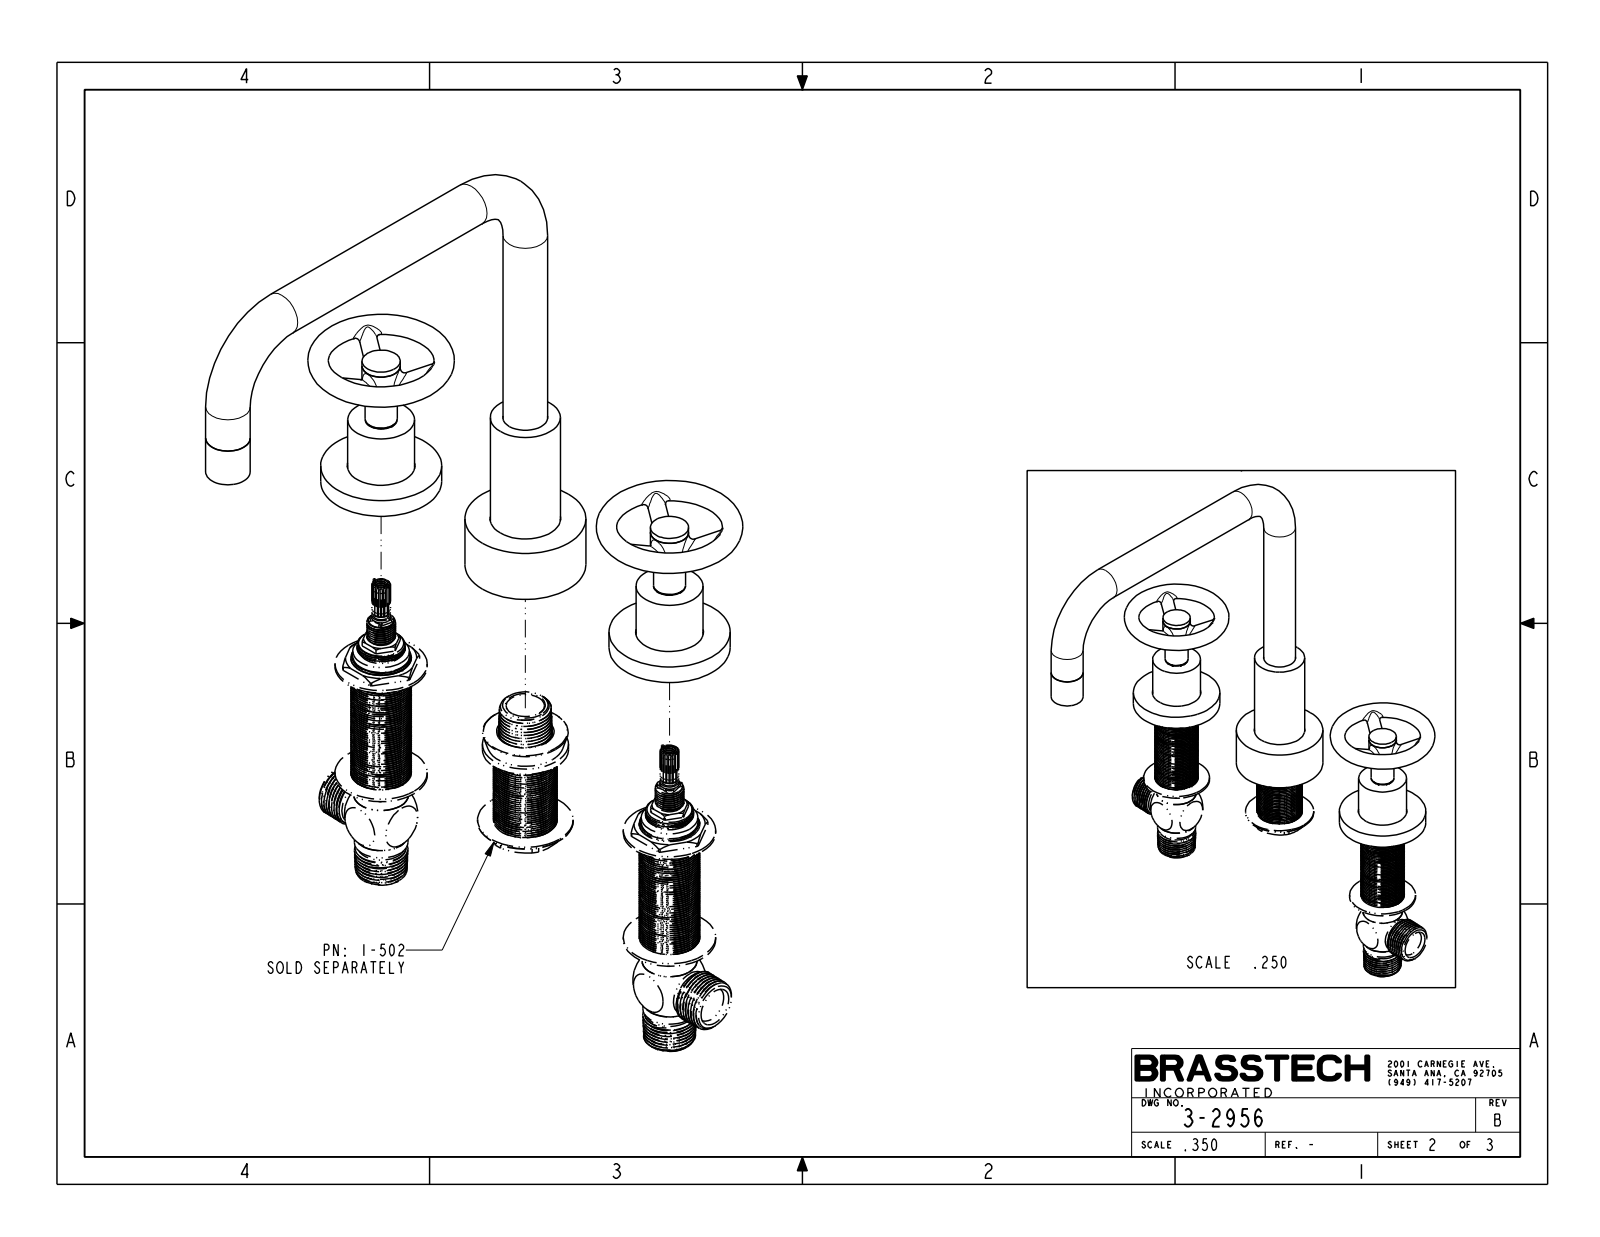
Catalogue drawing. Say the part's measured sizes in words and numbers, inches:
The part is named "3-2956". Its 3-D file was written by "CREO PARAMETRIC BY PTC INC, 2018400 (CONFIG_CONTROL_DESIGN)". It is 3 solids with 106 faces: 16 planar, 42 cylindrical and 48 other. Overall it measures 10.875 by 10.125 by 9.851 inches. Its volume is 27.91 cubic inches and its surface area 134.8 square inches. Round bosses or shafts: 6 of diameter 0.35, 3 of diameter 2.375, 3 of diameter 0.875, 2 of diameter 1.313, 2 of diameter 0.75, 2 of diameter 0.63, 2 of diameter 0.4, 1 of diameter 1.375. The main face-to-face distances are 0.375, 1.103, 0.728, 1.483, 1.108, 0.38, 2.893, 2.518, 1.79, 1.41.
